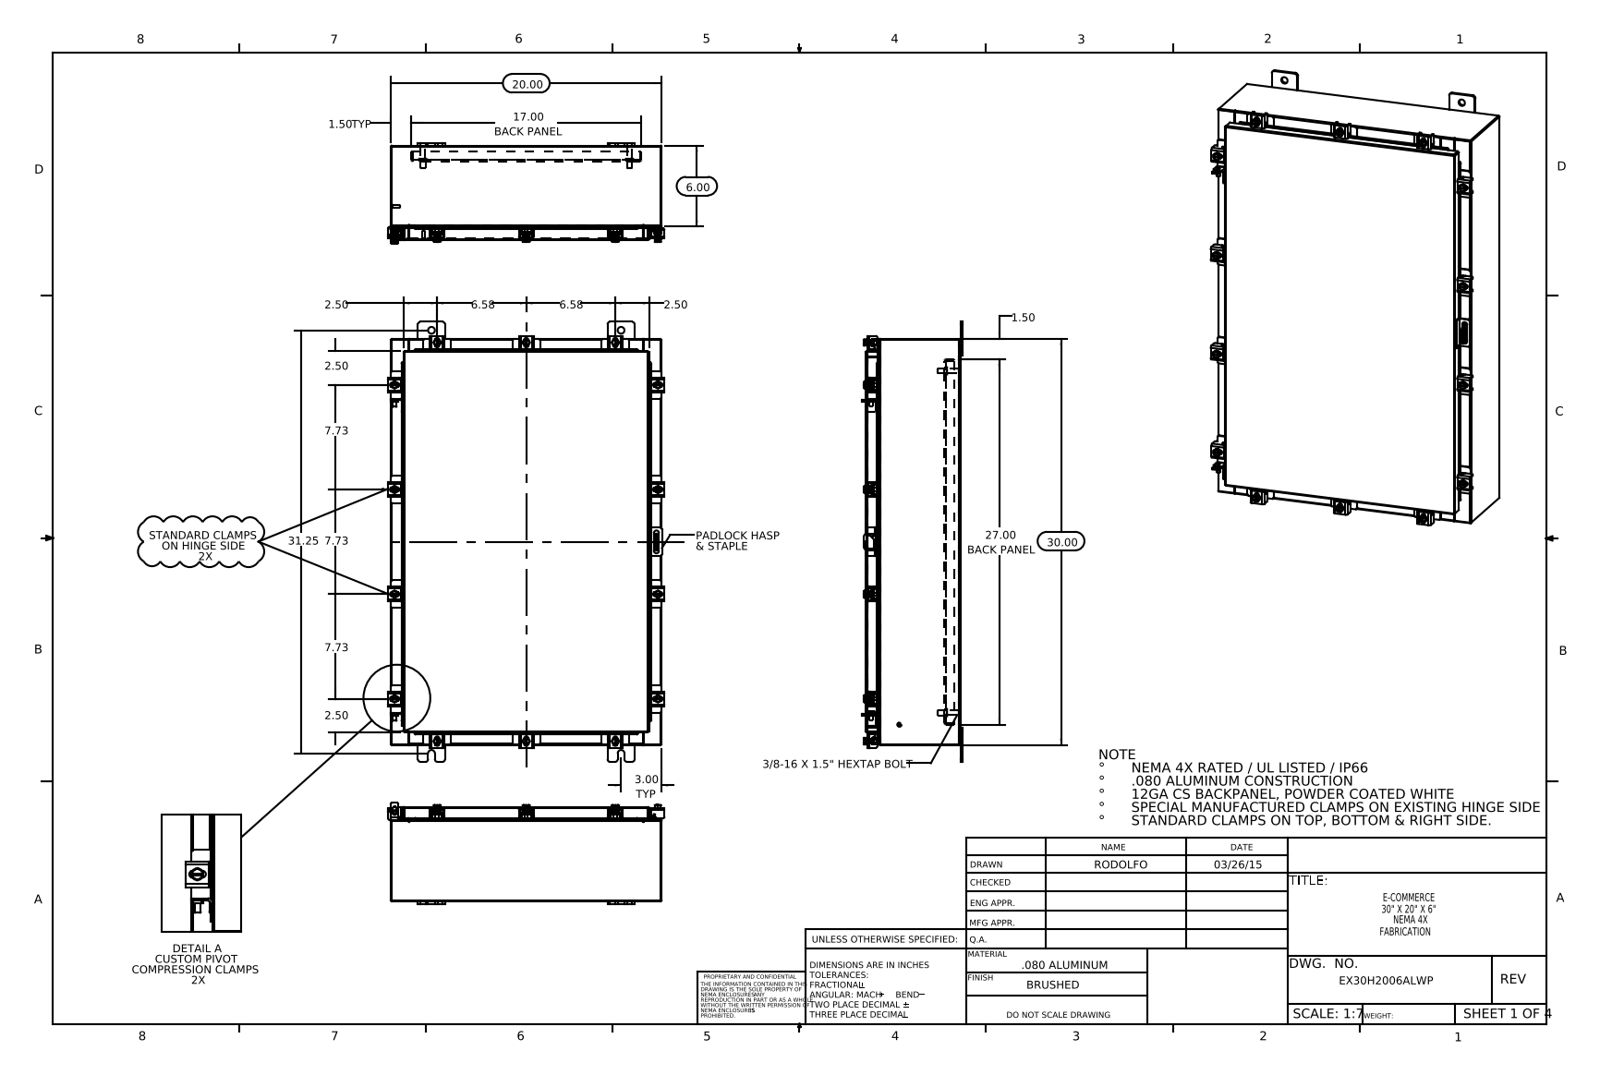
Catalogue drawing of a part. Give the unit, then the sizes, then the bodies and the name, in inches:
Units: inches
Overall size (bounding box): 32.5 × 20.421 × 7.453
Round holes (diameter × count): ⌀0.213 ×14, ⌀0.26 ×14, ⌀0.5 ×8, ⌀0.125 ×1, ⌀0.25 ×1
Round bosses / shafts (diameter × count): ⌀0.5 ×14, ⌀0.25 ×14, ⌀0.399 ×12, ⌀0.625 ×4, ⌀0.375 ×4, ⌀0.33 ×4, ⌀0.315 ×2, ⌀0.236 ×2
Partial cylindrical surfaces — rounded edges, fillets, slot ends (radius × count): R0.06 ×62, R0.141 ×28, R0.013 ×26, R0.12 ×26, R0.19 ×24, R0.088 ×22, R0.09 ×20, R0.05 ×19
Main face-to-face distances: 0.075, 6.9, 6.975, 6.826, 0.104, 1, 1.075, 5.826, 5.9, 1.179
Hole centre spacings: 2.347, 4.44, 16.602, 19.451, 24.31, 26.507, 27.371, 29.793
Volume: 214 in³ · Surface area: 5 301 in²
Bodies: 91 solids, 2272 faces (1211 planar, 885 cylindrical, 176 other)
Part name (STEP PRODUCT): EX30H2006ALWP Clamp Bracket; EX30H2006ALWP Standard Clamps; EX30H2006ALWP Padlock Staple; EX30H2006ALWP Bottom (+8 more)
STEP written by: SolidWorks 2014 (CONFIG_CONTROL_DESIGN)
